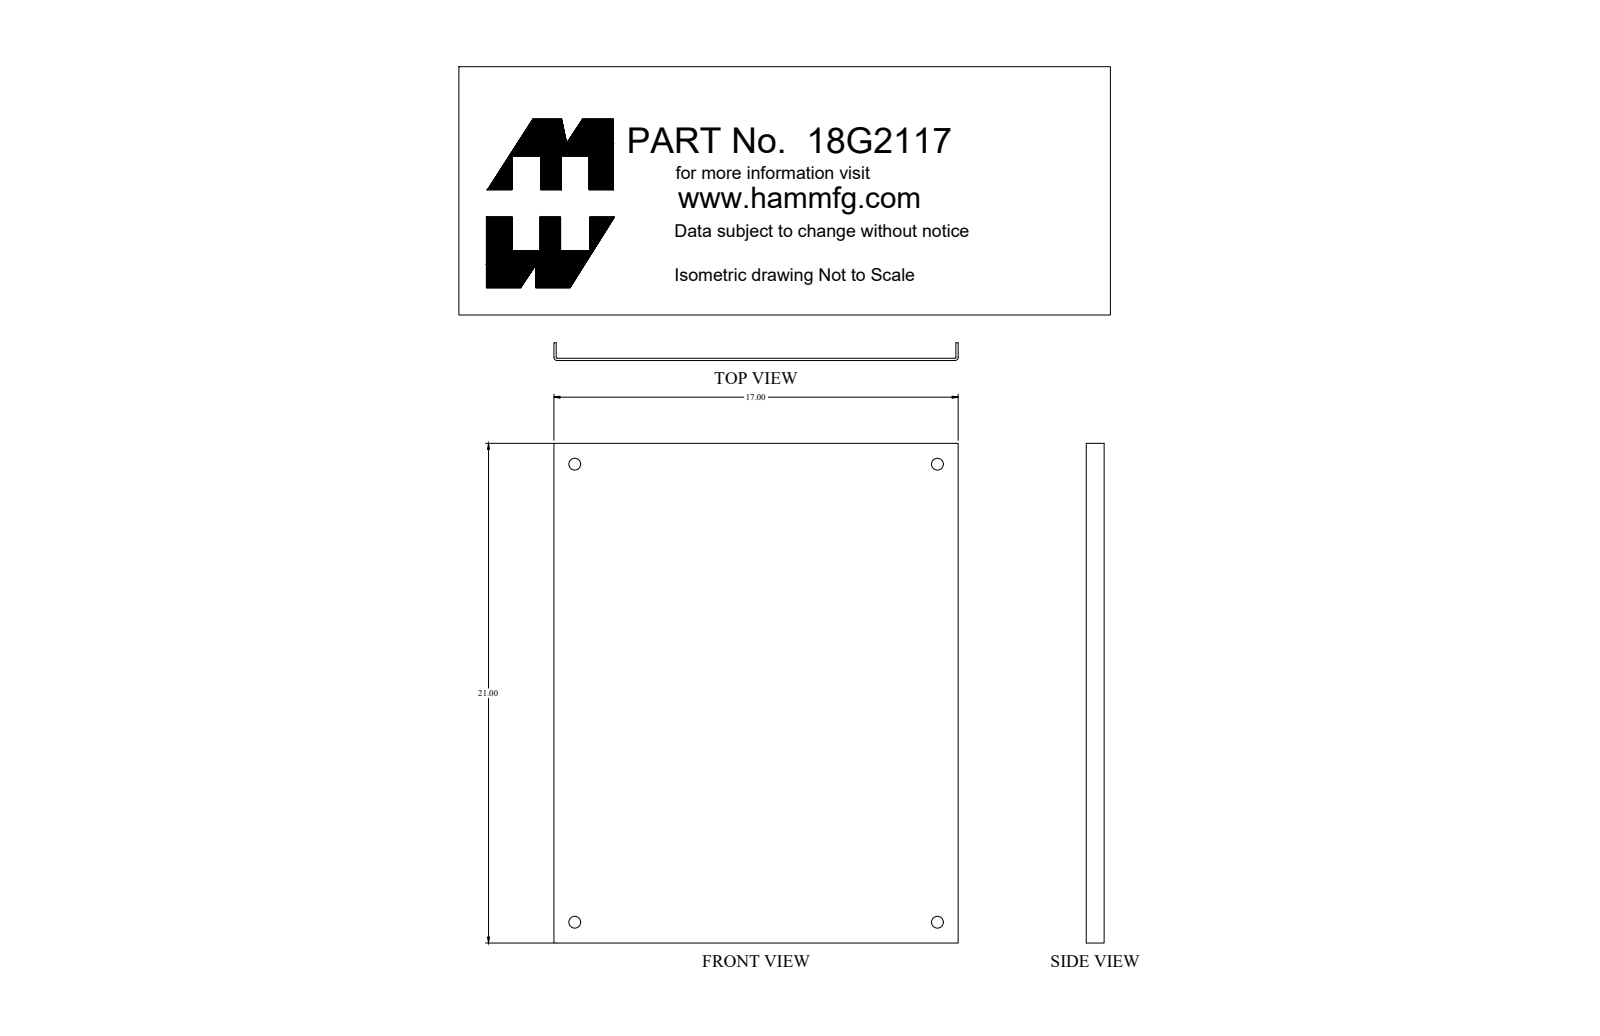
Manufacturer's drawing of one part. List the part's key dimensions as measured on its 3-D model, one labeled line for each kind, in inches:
Part name (STEP PRODUCT): 18G2117
STEP written by: SolidWorks 2018 (AUTOMOTIVE_DESIGN)
Units: inches
Bodies: 1 solid, 18 faces (10 planar, 8 cylindrical, 0 other)
Overall size (bounding box): 21 × 17 × 0.75
Volume: 36.32 in³ · Surface area: 772.7 in²
Round holes (diameter × count): ⌀0.5 ×4
Partial cylindrical surfaces — rounded edges, fillets, slot ends (radius × count): R0.03 ×2, R0.125 ×2
Main face-to-face distances: 0.095, 16.905, 17, 16.81, 0.75, 0.655, 21
Hole centre spacings: 15.25, 19.25, 24.558
